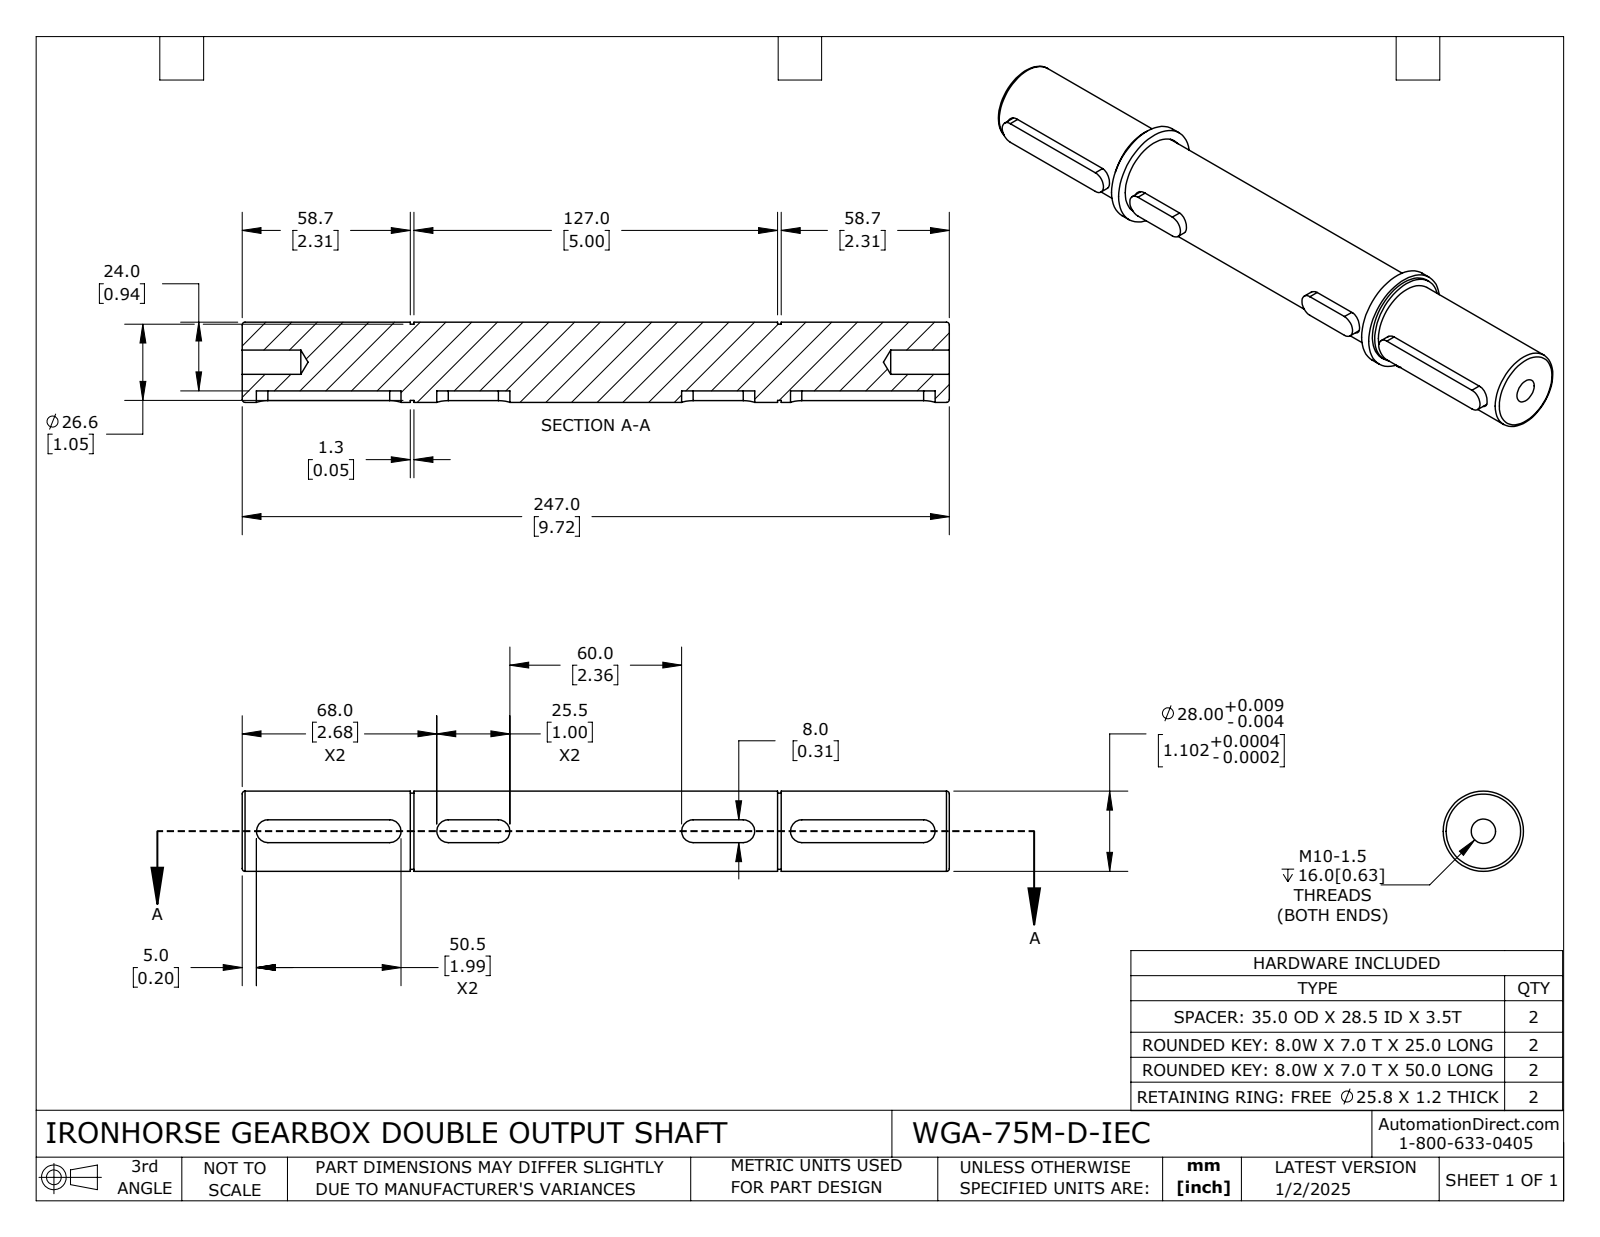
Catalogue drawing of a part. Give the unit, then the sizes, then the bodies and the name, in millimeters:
Units: millimetres
Overall size (bounding box): 247 × 35.3 × 35
Round holes (diameter × count): ⌀1.9 ×2, ⌀8.5 ×1, ⌀26.4 ×1, ⌀28.5 ×1
Round bosses / shafts (diameter × count): ⌀35 ×1, ⌀31.35 ×1, ⌀28 ×1, ⌀26.6 ×1
Partial cylindrical surfaces — rounded edges, fillets, slot ends (radius × count): R4 ×12, R0.5 ×2, R2.8 ×2
Main face-to-face distances: 8, 7, 60, 187, 63.5, 183.5, 3.5, 123.5, 127, 58.85
Hole centre spacings: 15.9, 3.04
Volume: 155 883 mm³ · Surface area: 34 178 mm²
Bodies: 9 solids, 136 faces (54 planar, 74 cylindrical, 8 other)
Part name (STEP PRODUCT): WGA-75M-D-IEC
STEP written by: SolidWorks 2024 (CONFIG_CONTROL_DESIGN)
